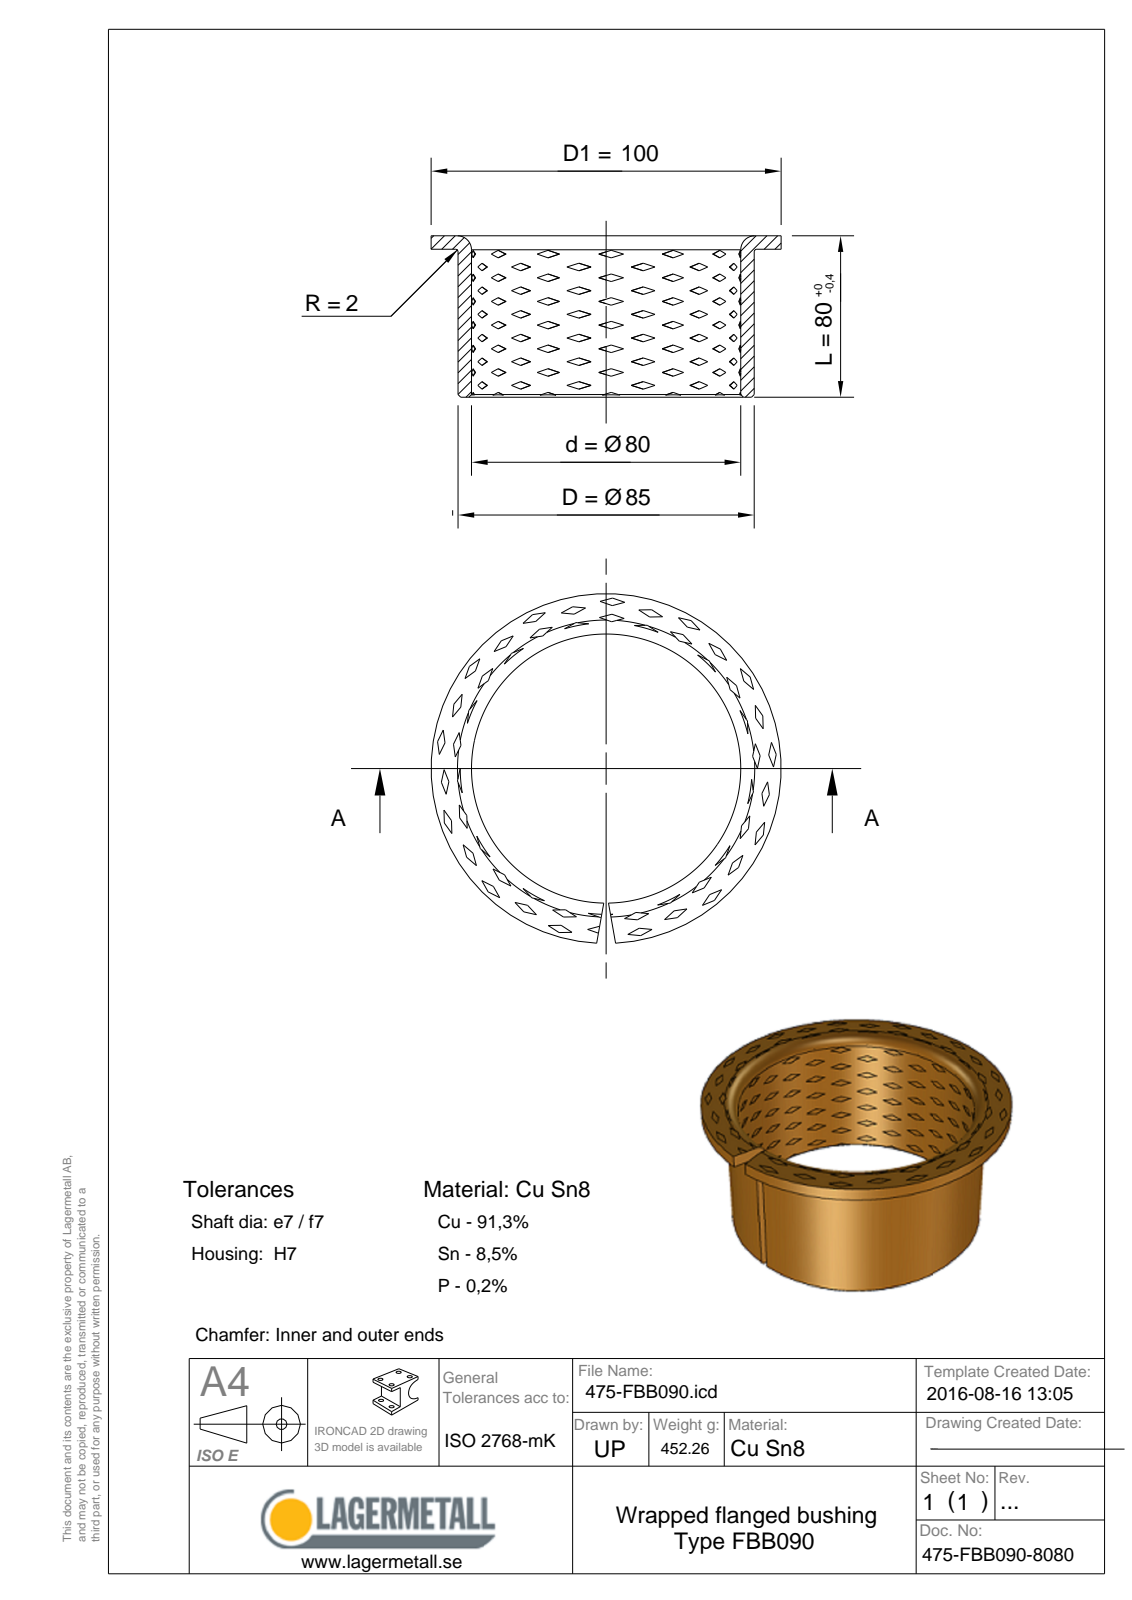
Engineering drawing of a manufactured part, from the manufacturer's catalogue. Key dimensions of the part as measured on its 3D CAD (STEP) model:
Part name (STEP PRODUCT): 475-FBB090-8080
STEP written by: Spatial InterOp 3D (CONFIG_CONTROL_DESIGN)
Units: millimetres
Bodies: 1 solid, 12 faces (5 planar, 3 cylindrical, 4 other)
Overall size (bounding box): 100 × 99.95 × 80
Volume: 55 834 mm³ · Surface area: 46 440 mm²
Round holes (diameter × count): ⌀80 ×1
Round bosses / shafts (diameter × count): ⌀100 ×1, ⌀85 ×1
Main face-to-face distances: 2.5, 77.5, 80
